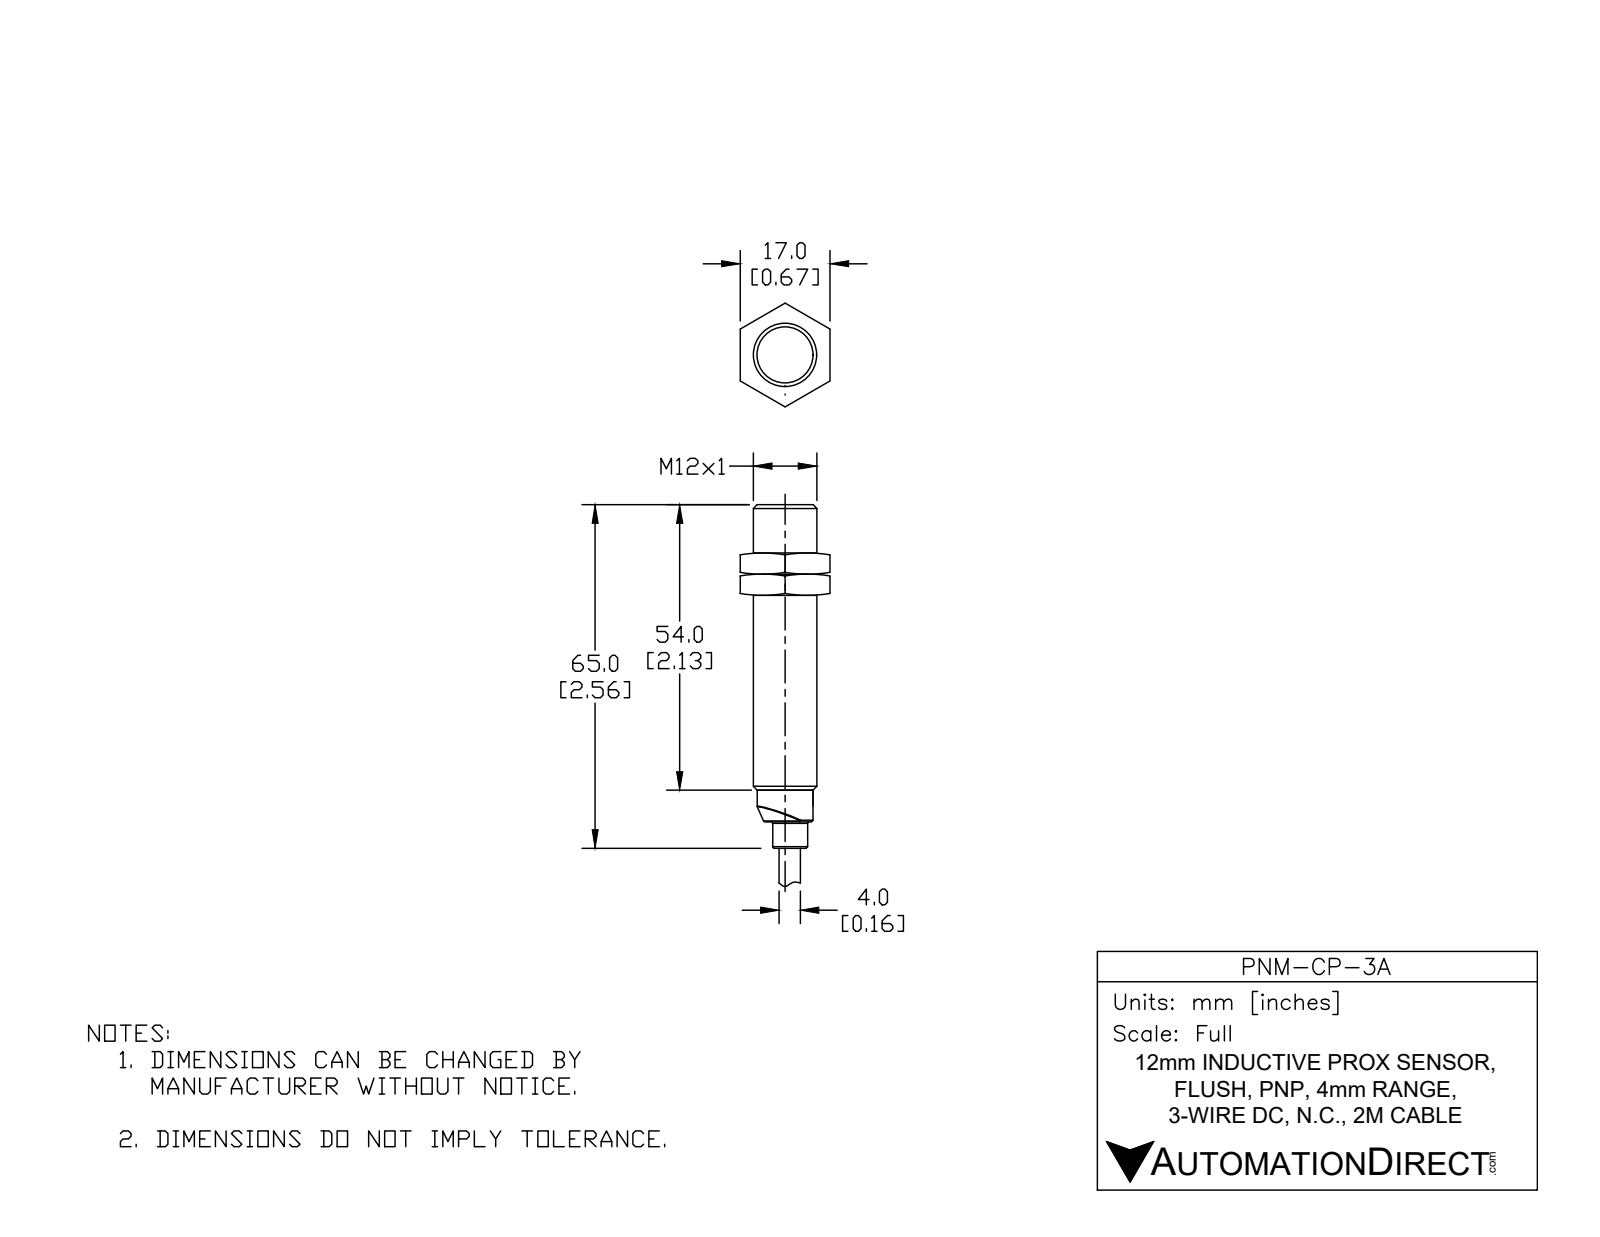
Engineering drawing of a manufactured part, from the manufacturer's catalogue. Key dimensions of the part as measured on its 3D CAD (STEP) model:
Part name (STEP PRODUCT): PNM-CP-3A
STEP written by: SolidWorks 2017 (AUTOMOTIVE_DESIGN)
Units: inches
Bodies: 1 solid, 68 faces (21 planar, 19 cylindrical, 28 other)
Overall size (bounding box): 4.559 × 0.472 × 0.472
Volume: 0.452 in³ · Surface area: 4.972 in²
Round holes (diameter × count): ⌀0.161 ×1, ⌀0.401 ×1
Round bosses / shafts (diameter × count): ⌀0.472 ×1, ⌀0.417 ×1, ⌀0.415 ×1, ⌀0.384 ×1, ⌀0.26 ×1, ⌀0.157 ×1
Partial cylindrical surfaces — rounded edges, fillets, slot ends (radius × count): R0.091 ×1
Main face-to-face distances: 2.362, 2.559, 0.197, 4.559, 2.197, 2, 0.022, 2.34, 2.537, 4.537
Hole centre spacings: 0.039
